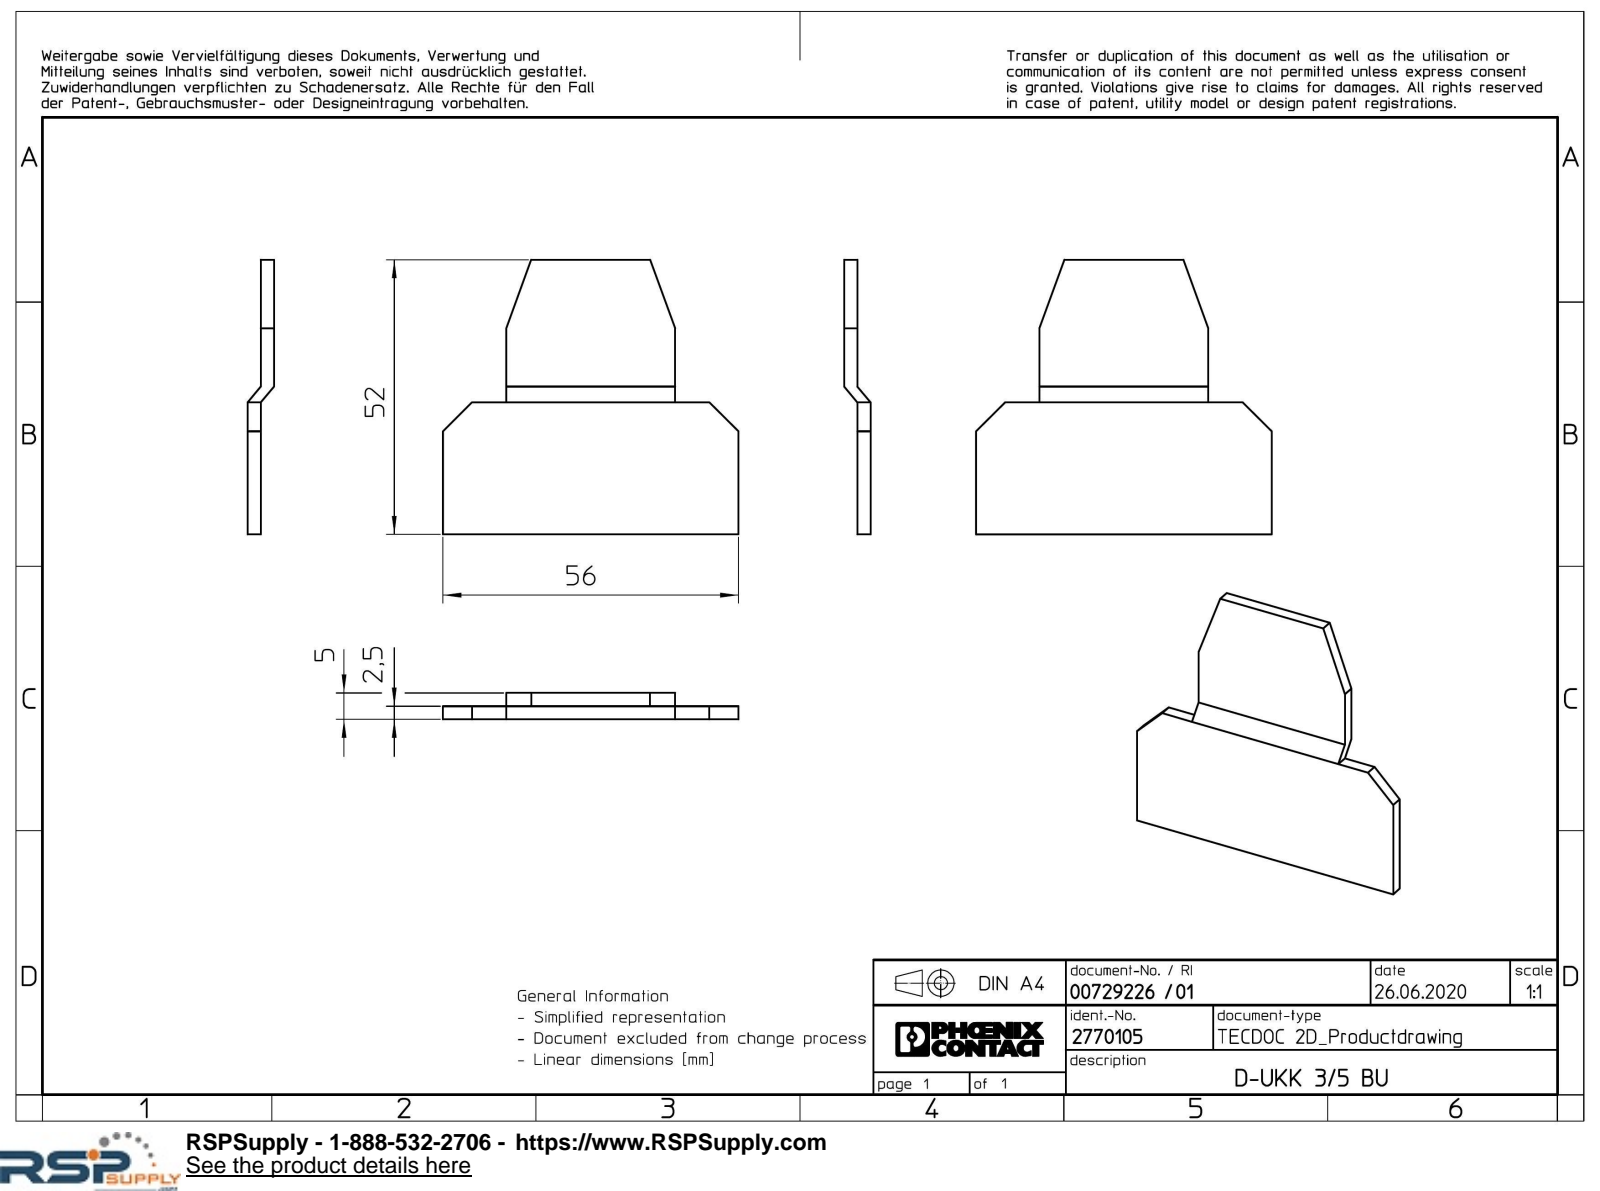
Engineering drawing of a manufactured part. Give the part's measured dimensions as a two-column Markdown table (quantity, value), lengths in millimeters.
| quantity | value |
| --- | --- |
| part name | D-UKK_3_5_BU-select |
| STEP written by | Creo Elements/Direct Modeling 20.1A 29-Sep-2018 (C) Parametric Technology GmbH (AUTOMOTIVE_DESIGN) |
| units | millimeters |
| bodies | 1 solid, 18 faces (18 planar, 0 cylindrical, 0 other) |
| overall size | 56 × 52 × 5 |
| volume | 5 431 mm³ |
| surface area | 4 907 mm² |
| main face-to-face distances | 2.5, 5, 1.92, 12, 44, 52, 56, 32, 25, 27 |
